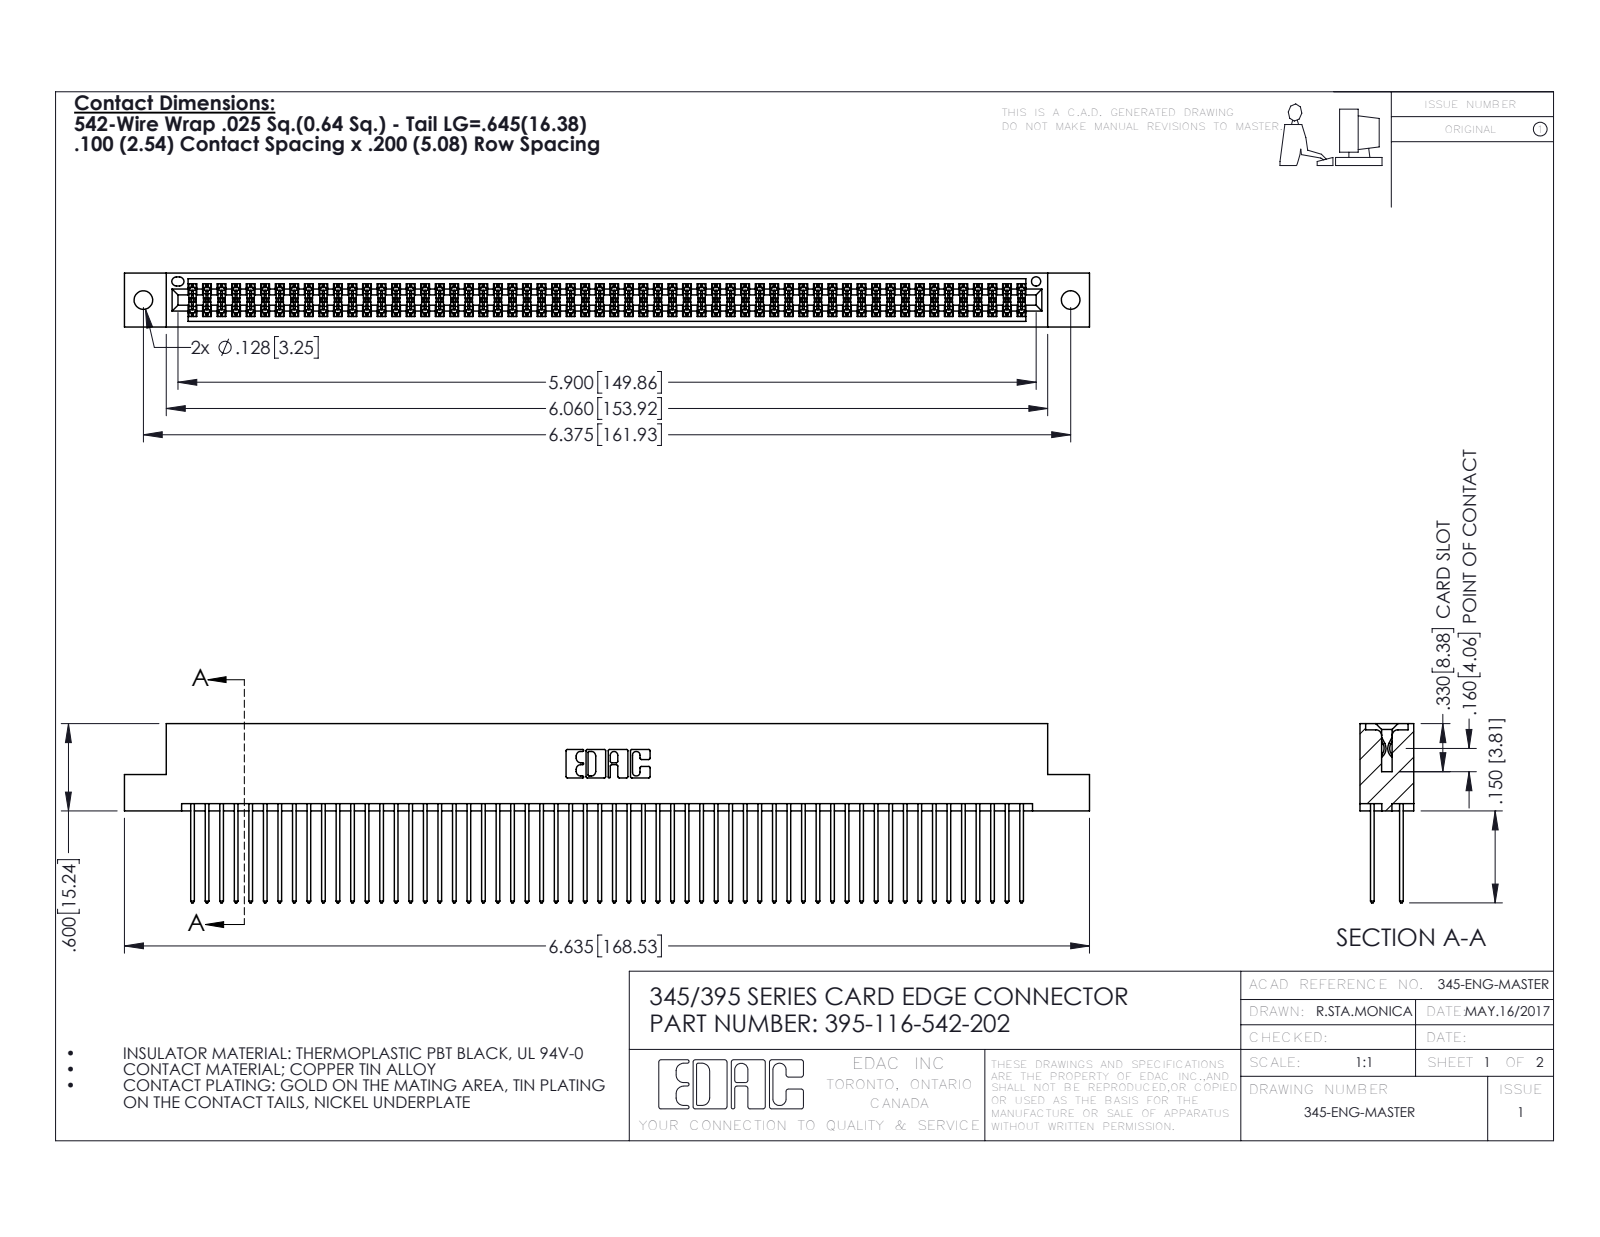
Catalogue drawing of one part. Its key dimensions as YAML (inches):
part_name: "395-116-542-202; 345-292-001_345-293-142; 345 Part_Flush Mounting Lugs - 0.128 Dia"
step_written_by: "SolidWorks 2016 (CONFIG_CONTROL_DESIGN)"
units: inches
bodies: {solids: 117, faces: 5926, planar: 3908, cylindrical: 2018, other: 0}
overall_size: [6.635, 1.232, 0.37]
volume: 1.039
surface_area: 42.98
round_holes:
  - {diameter: 0.128, count: 2}
  - {diameter: 0.064, count: 1}
partial_cylinders:
  - {radius: 0.006, count: 174}
  - {radius: 0.01, count: 116}
  - {radius: 0.01, count: 22}
  - {radius: 0.007, count: 6}
  - {radius: 0.031, count: 6}
  - {radius: 0.026, count: 3}
  - {radius: 0.014, count: 2}
  - {radius: 0.019, count: 2}
face_to_face_distances: [0.298, 0.072, 0.2, 0.098, 0.272, 0.025, 0.225, 0.37, 0.175, 0.149]
hole_center_spacings: [0.27, 6.139, 6.375]
